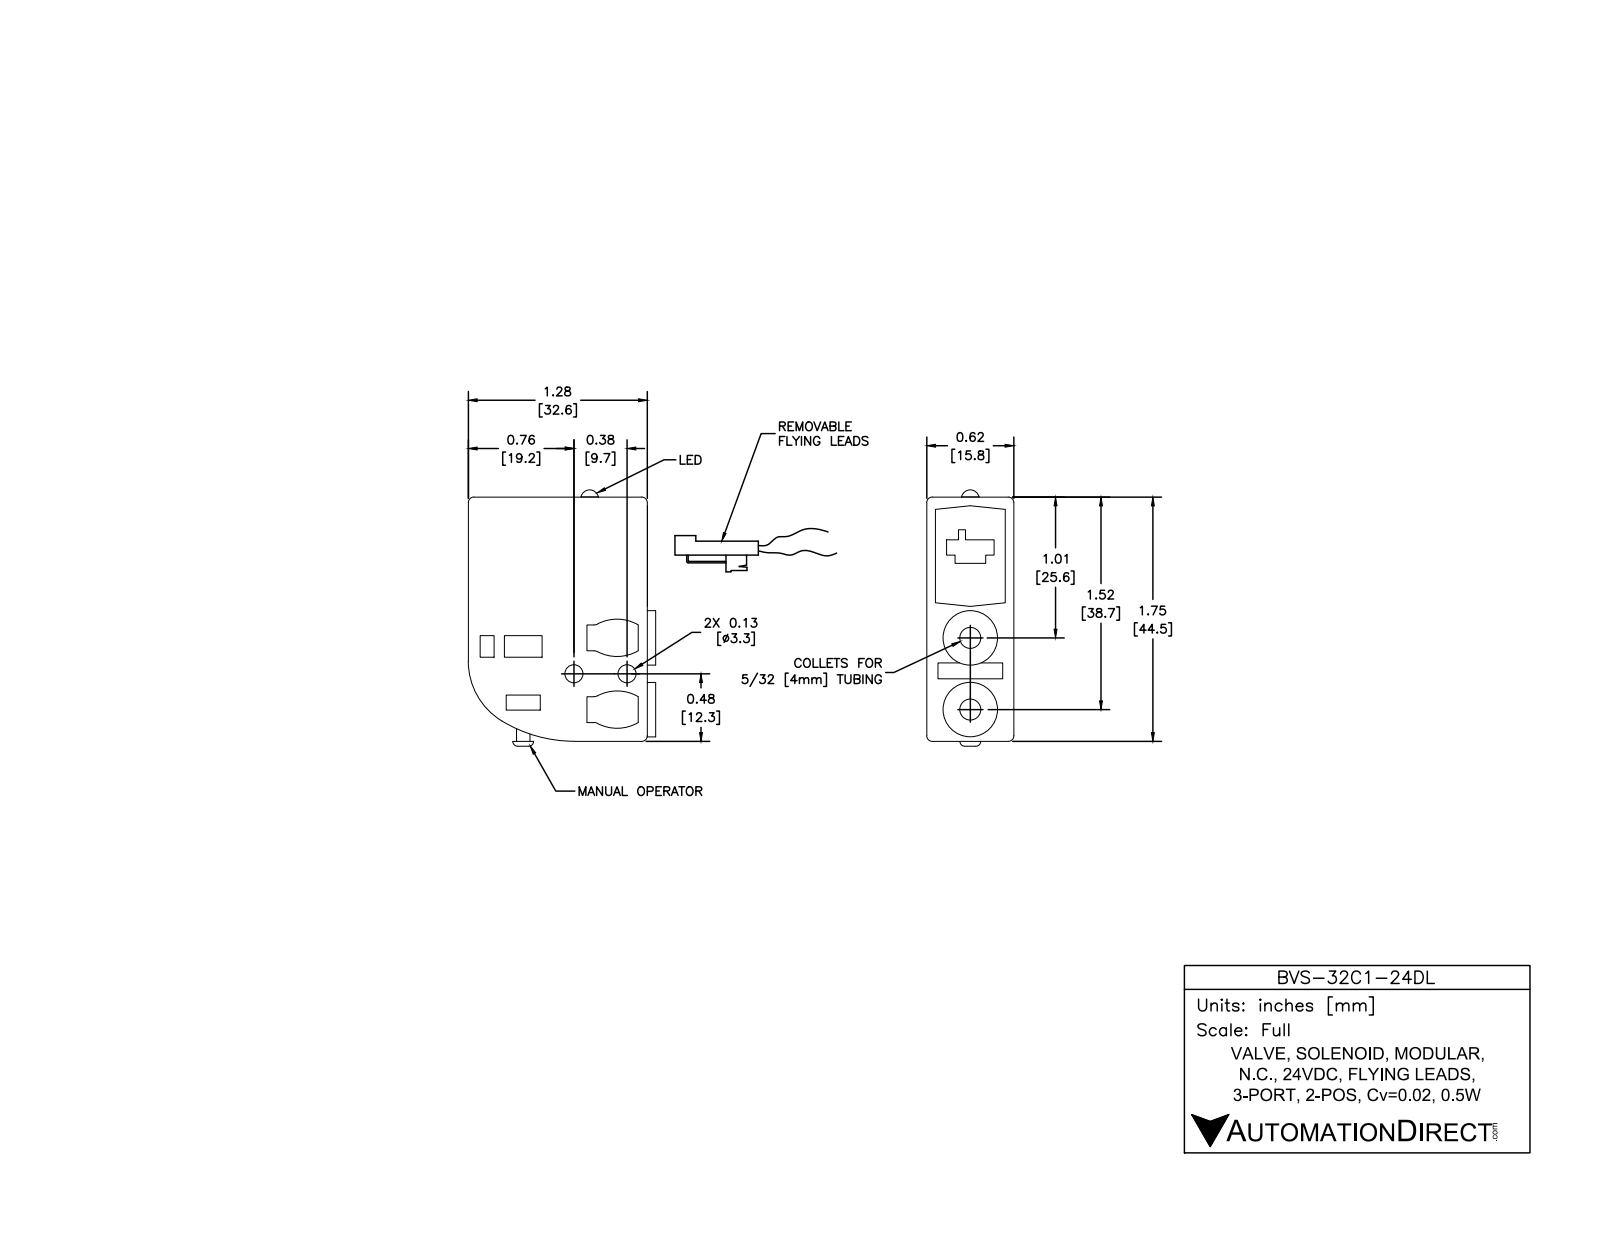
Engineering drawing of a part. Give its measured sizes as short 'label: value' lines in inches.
name: BVS-32C1-24DL
written by: SolidWorks 2016 (AUTOMOTIVE_DESIGN)
unit: in
bodies: 1 solid, 149 faces (83 planar, 54 cylindrical, 12 other)
size: 1.84 × 1.788 × 0.62
volume: 1.259 in³; area: 10.37 in²
holes: 2× ⌀0.13, 2× ⌀0.15, 2× ⌀0.25, 1× ⌀0.05
bosses: 6× ⌀0.06, 2× ⌀0.39, 1× ⌀0.1
rounds: 4× R0.05, 4× R0.3, 3× R0.04, 1× R0.5, 1× R1
face distances: 0.62, 0.1, 1.29, 0.52, 1.291, 1.75, 1, 0.15, 0.06, 1.35
hole spacings: 0.06, 0.38, 0.45, 0.51
